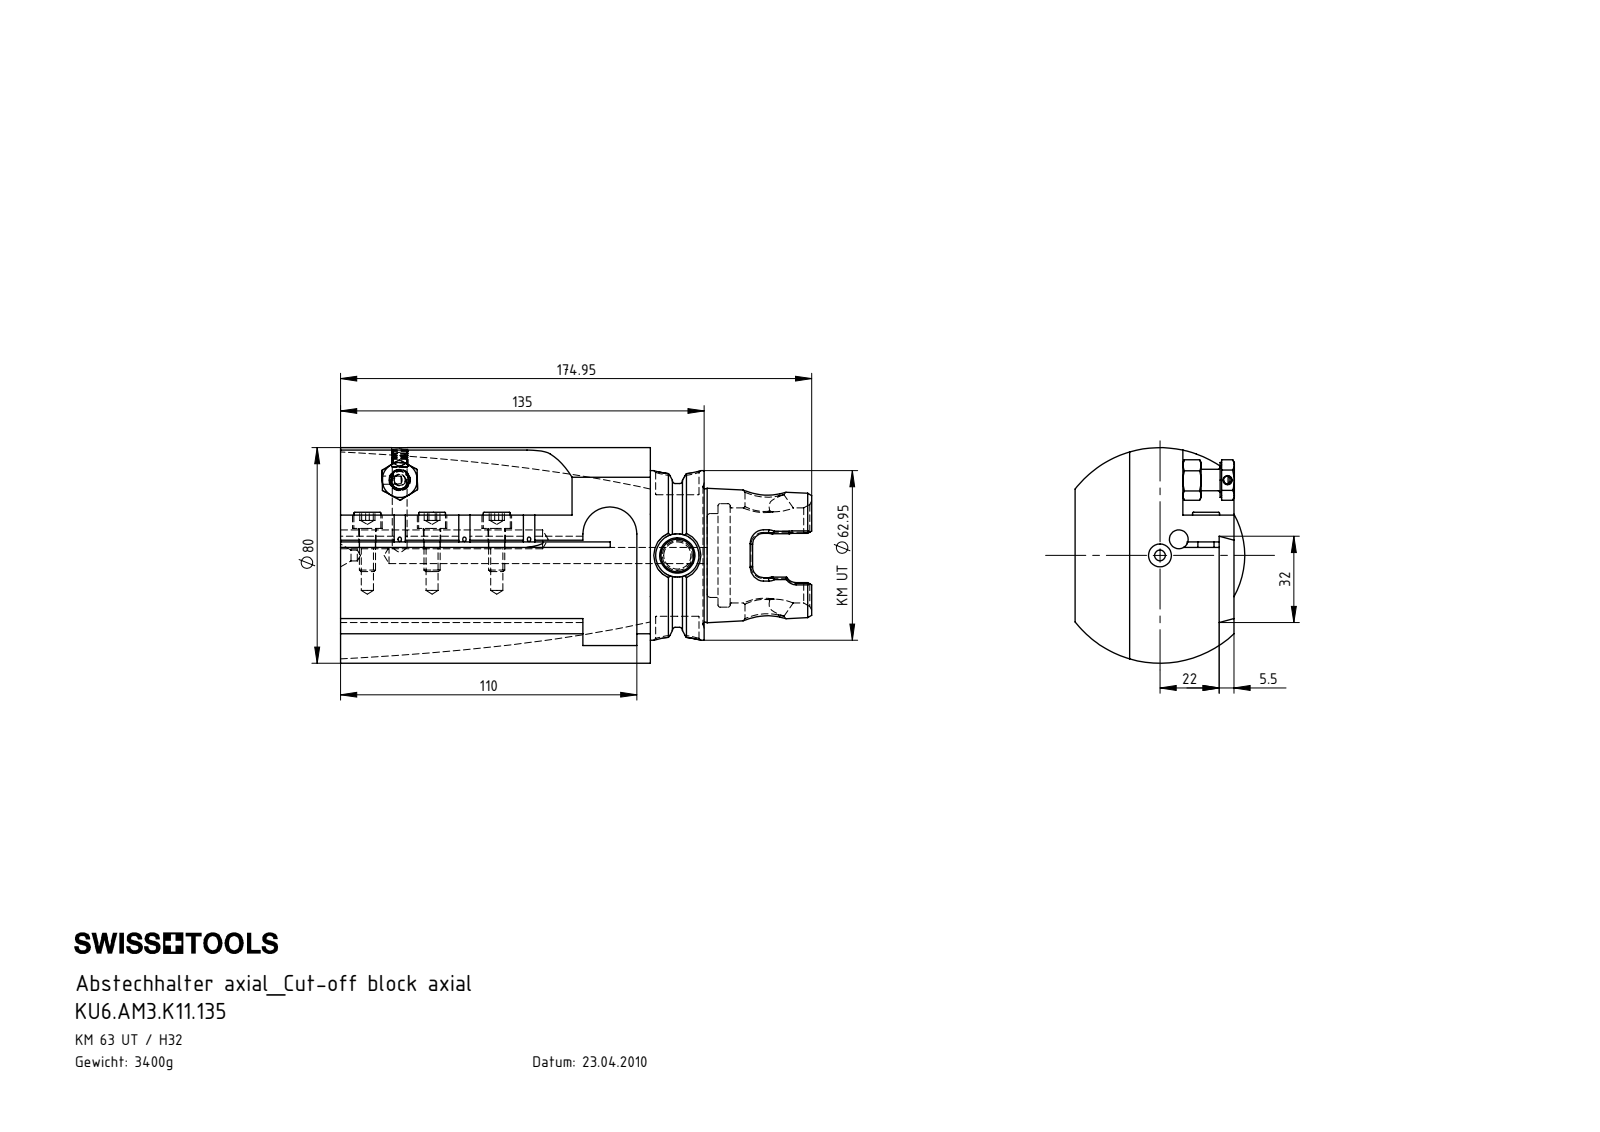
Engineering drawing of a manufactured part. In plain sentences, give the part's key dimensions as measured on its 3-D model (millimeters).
The part is named "AM3-ER1.001.020_PreviewCfg; ISO 4035 - M8_PreviewCfg; ISO 4762 - M6 x 16_PreviewCfg; KU6-AM3.K11.135_B (+2 more)". Its 3-D file was written by "SolidWorks 2017 (CONFIG_CONTROL_DESIGN)". It is 8 solids with 493 faces: 155 planar, 118 cylindrical and 220 other. Overall it measures 174.95 by 80 by 62.95 millimeters. Its volume is 431 546 cubic millimeters and its surface area 63 246 square millimeters. Round holes: 4 of diameter 6.4, 3 of diameter 4.5, 3 of diameter 11, 2 of diameter 4, 2 of diameter 7, 2 of diameter 16.05, 1 of diameter 3, 1 of diameter 5, 1 of diameter 5.5, 1 of diameter 6, 1 of diameter 10.1, 1 of diameter 12.1. Round bosses or shafts: 4 of diameter 6, 3 of diameter 10, 1 of diameter 62.95, 1 of diameter 13, 1 of diameter 8. Partial cylindrical surfaces (rounded edges, fillets, slot ends): 6 of radius 4, 3 of radius 2.1, 2 of radius 7.04, 2 of radius 10, 1 of radius 0.8, 1 of radius 27.85, 1 of radius 40, 1 of radius 77.5. The main face-to-face distances are 5.5, 19, 13.5, 113, 12, 2, 22, 10, 135, 5. The hole center spacings are 20.89, 24, 9.22, 32.35, 39.85, 48, 69.2, 92.64.
